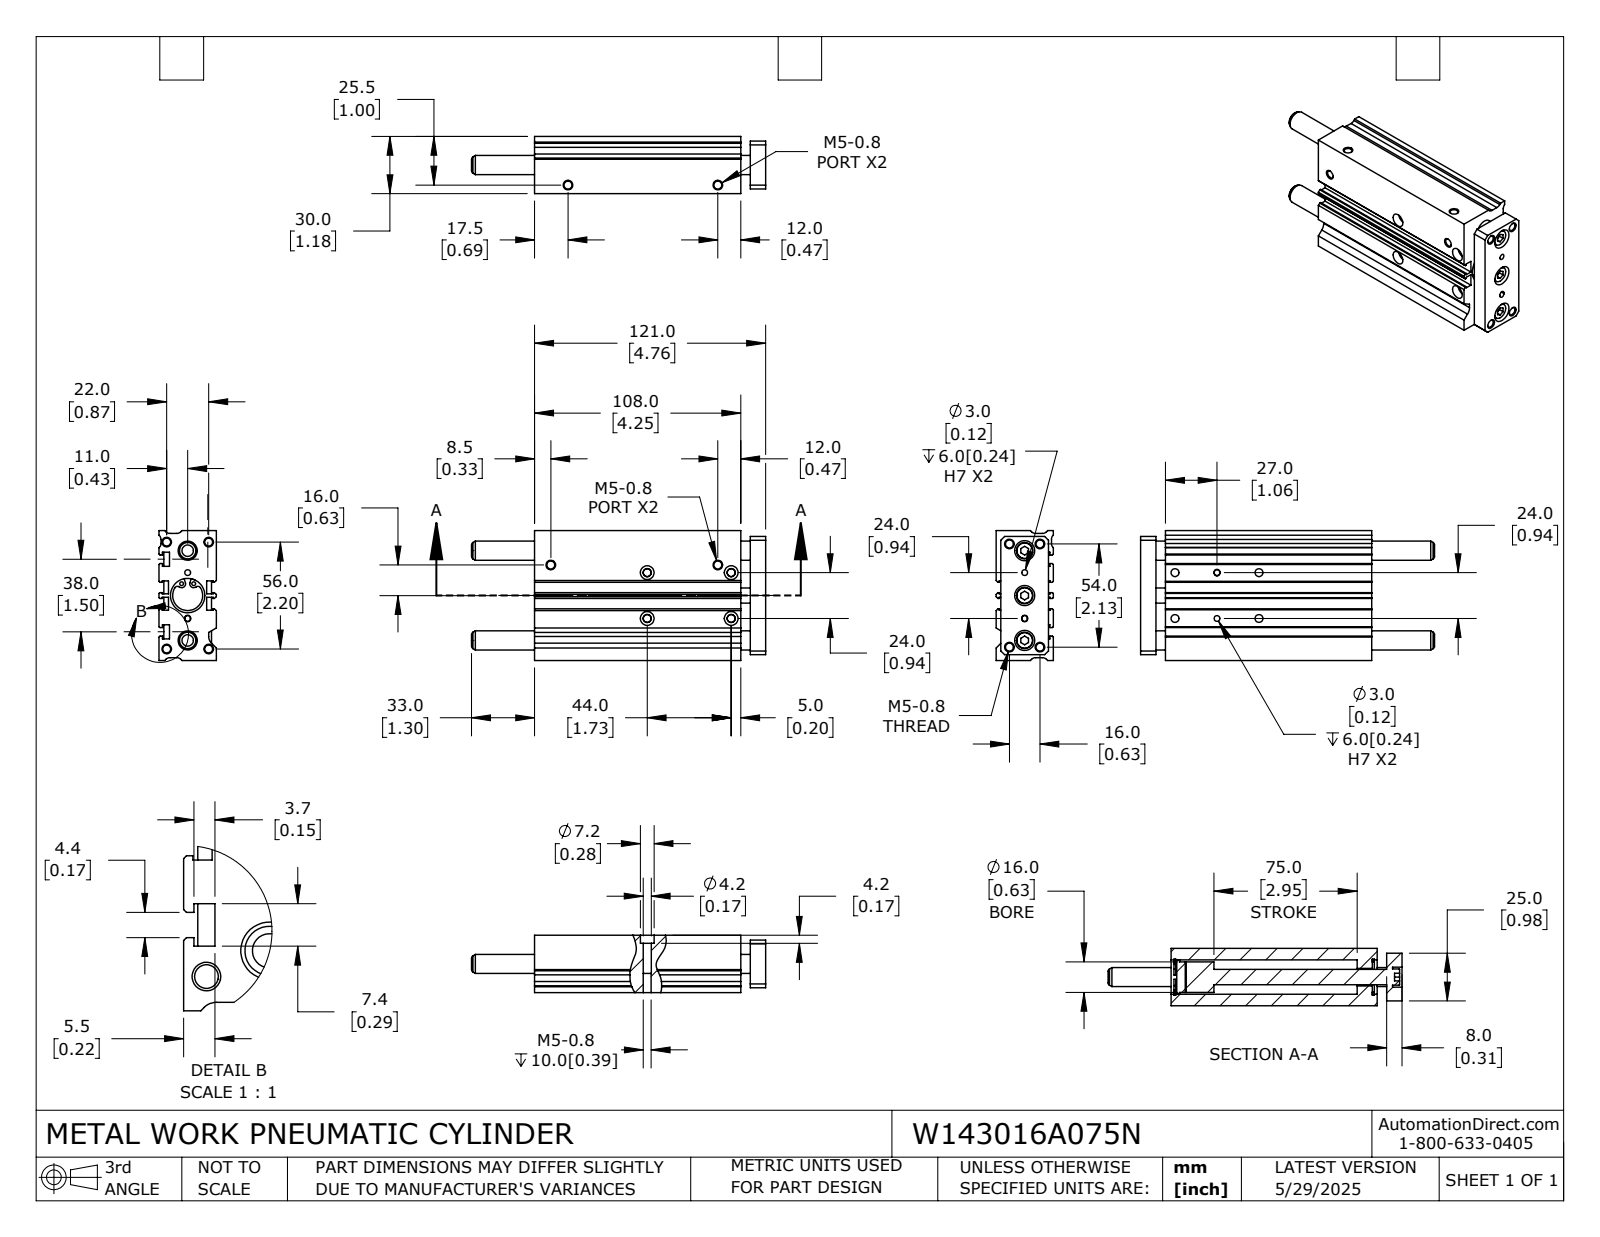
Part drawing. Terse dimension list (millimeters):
name: W143016A075N; W143016A075N_BODY; W143016A075N_ROD
written by: SolidWorks 2024 (CONFIG_CONTROL_DESIGN)
unit: mm
bodies: 5 solids, 344 faces (169 planar, 137 cylindrical, 38 other)
size: 154 × 68 × 30
volume: 189 328 mm³; area: 68 675 mm²
holes: 16× ⌀4.13, 4× ⌀2, 4× ⌀3, 4× ⌀4.2, 4× ⌀7.2, 3× ⌀10.5, 2× ⌀10, 1× ⌀9.2, 1× ⌀15.7, 1× ⌀18
bosses: 3× ⌀8.5, 2× ⌀19, 1× ⌀16, 1× ⌀8
rounds: 6× R3, 4× R1.5, 4× R1.58, 4× R2.07, 1× R5
face distances: 5, 30, 25, 2.5, 1.5, 68, 0.5, 5.5, 8, 19.5
hole spacings: 22, 3.16, 6.62, 6.95, 8.73, 11.88, 17, 17.6
